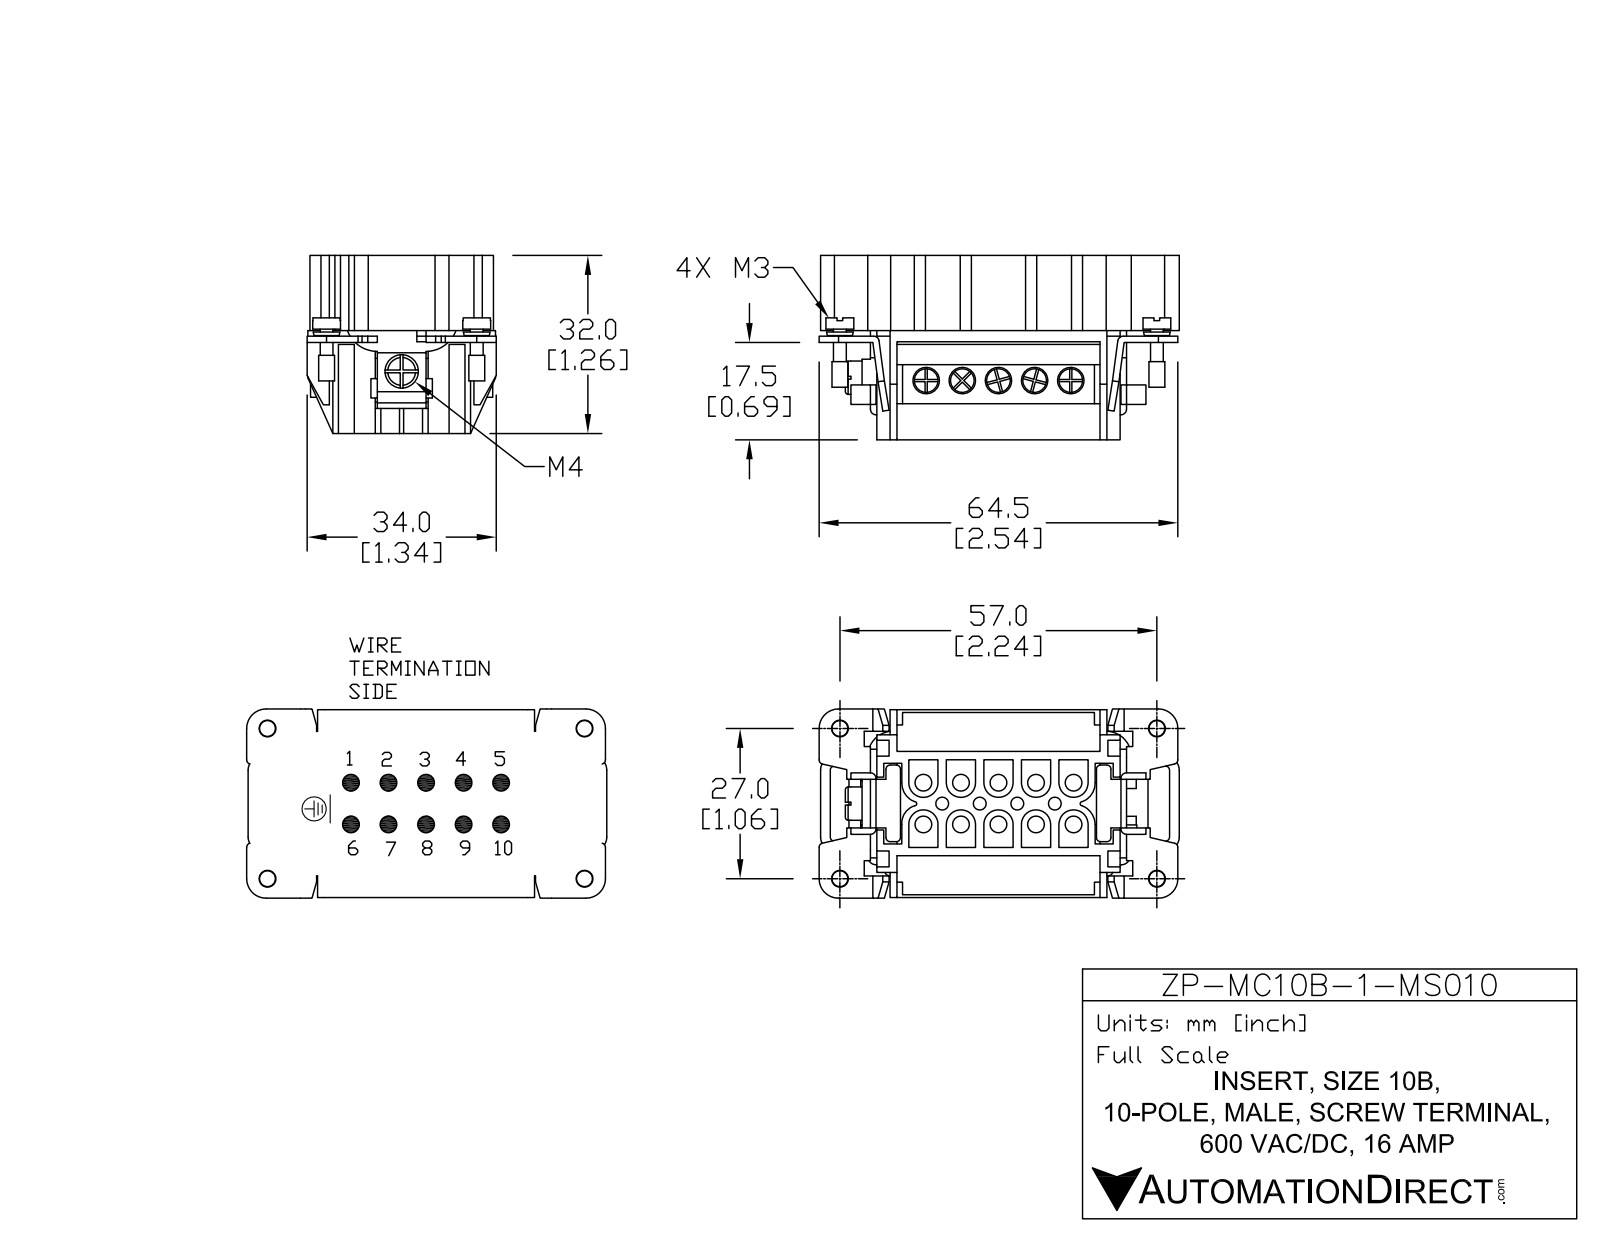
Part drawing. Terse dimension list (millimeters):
name: ZP-10B-10-MS-INSERT
written by: SolidWorks 2011 (AUTOMOTIVE_DESIGN)
unit: mm
bodies: 5 solids, 730 faces (526 planar, 176 cylindrical, 28 other)
size: 64.76 × 34 × 32
volume: 20 159 mm³; area: 23 603 mm²
holes: 11× ⌀3, 5× ⌀4.75, 4× ⌀2.3, 4× ⌀3.01
bosses: 10× ⌀2.5, 4× ⌀5, 4× ⌀2.85, 4× ⌀2.3, 1× ⌀6
rounds: 24× R0.75, 12× R1, 10× R2.62, 10× R2.62, 6× R0.25, 6× R2, 4× R2.5, 4× R3.5
face distances: 1.75, 2.5, 13.5, 12, 1.15, 7, 3.62, 1, 5, 4.5
hole spacings: 6.75, 5.04, 5.06, 10.09, 13.5, 10.78, 10.81, 15.44
